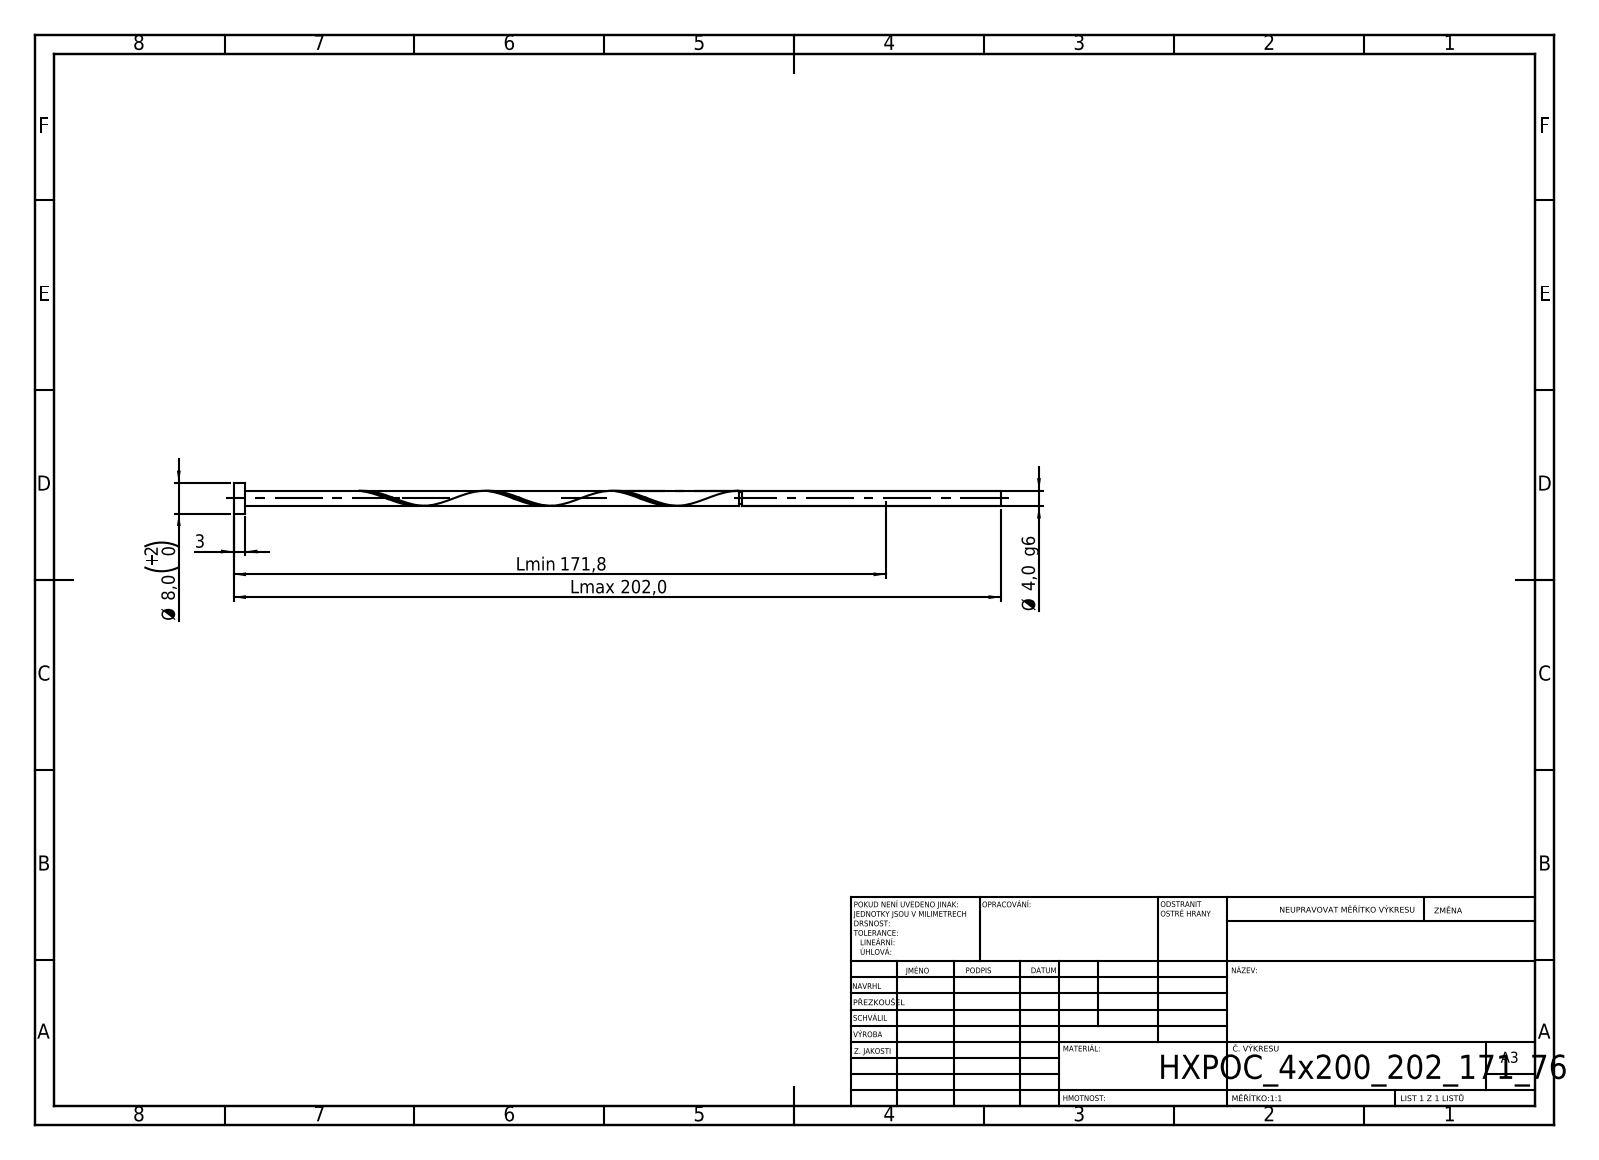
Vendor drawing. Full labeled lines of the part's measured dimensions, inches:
STEP written by: SolidWorks 2019 (CONFIG_CONTROL_DESIGN)
Units: inches
Bodies: 1 solid, 21 faces (6 planar, 14 cylindrical, 1 other)
Overall size (bounding box): 7.953 × 0.315 × 0.315
Volume: 0.16 in³ · Surface area: 4.224 in²
Round bosses / shafts (diameter × count): ⌀0.315 ×1, ⌀0.157 ×1, ⌀0.126 ×1
Main face-to-face distances: 0.118, 7.953, 7.835, 5.266, 5.148, 2.687, 5.235, 5.117, 0.031, 2.718
